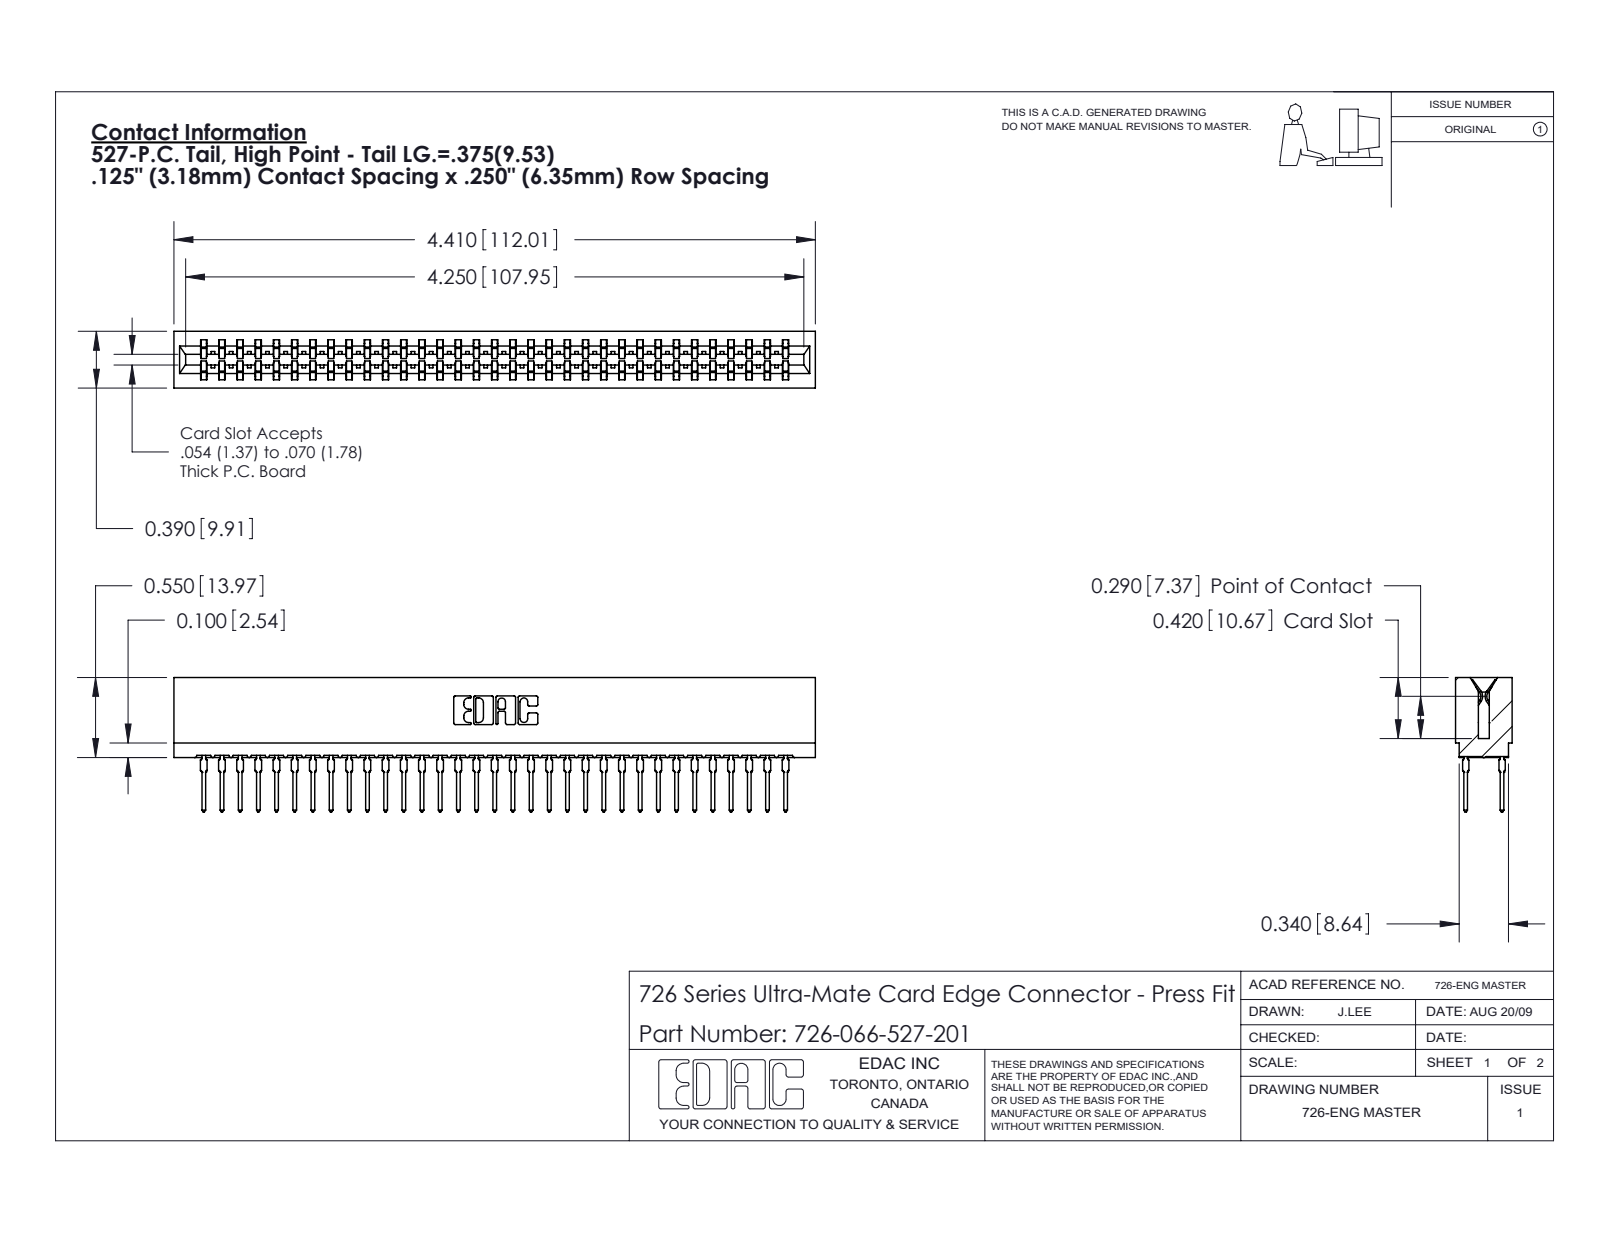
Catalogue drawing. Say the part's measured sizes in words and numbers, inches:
The part is named "746-292-001_527; 726 Part_.515 Slot Depth - 01; 726-066-527-201". Its 3-D file was written by "SolidWorks 2020 (CONFIG_CONTROL_DESIGN)". It is 67 solids with 6004 faces: 3091 planar, 1197 cylindrical and 1716 other. Overall it measures 4.41 by 0.924 by 0.39 inches. Its volume is 0.638 cubic inches and its surface area 27.59 square inches. Partial cylindrical surfaces (rounded edges, fillets, slot ends): 132 of radius 0.021, 34 of radius 0.015, 22 of radius 0.01, 8 of radius 0.005, 8 of radius 0.011, 6 of radius 0.007, 6 of radius 0.031, 3 of radius 0.026. The main face-to-face distances are 0.057, 0.333, 0.25, 0.025, 0.307, 0.39, 0.083, 0.275, 0.5, 0.75.
